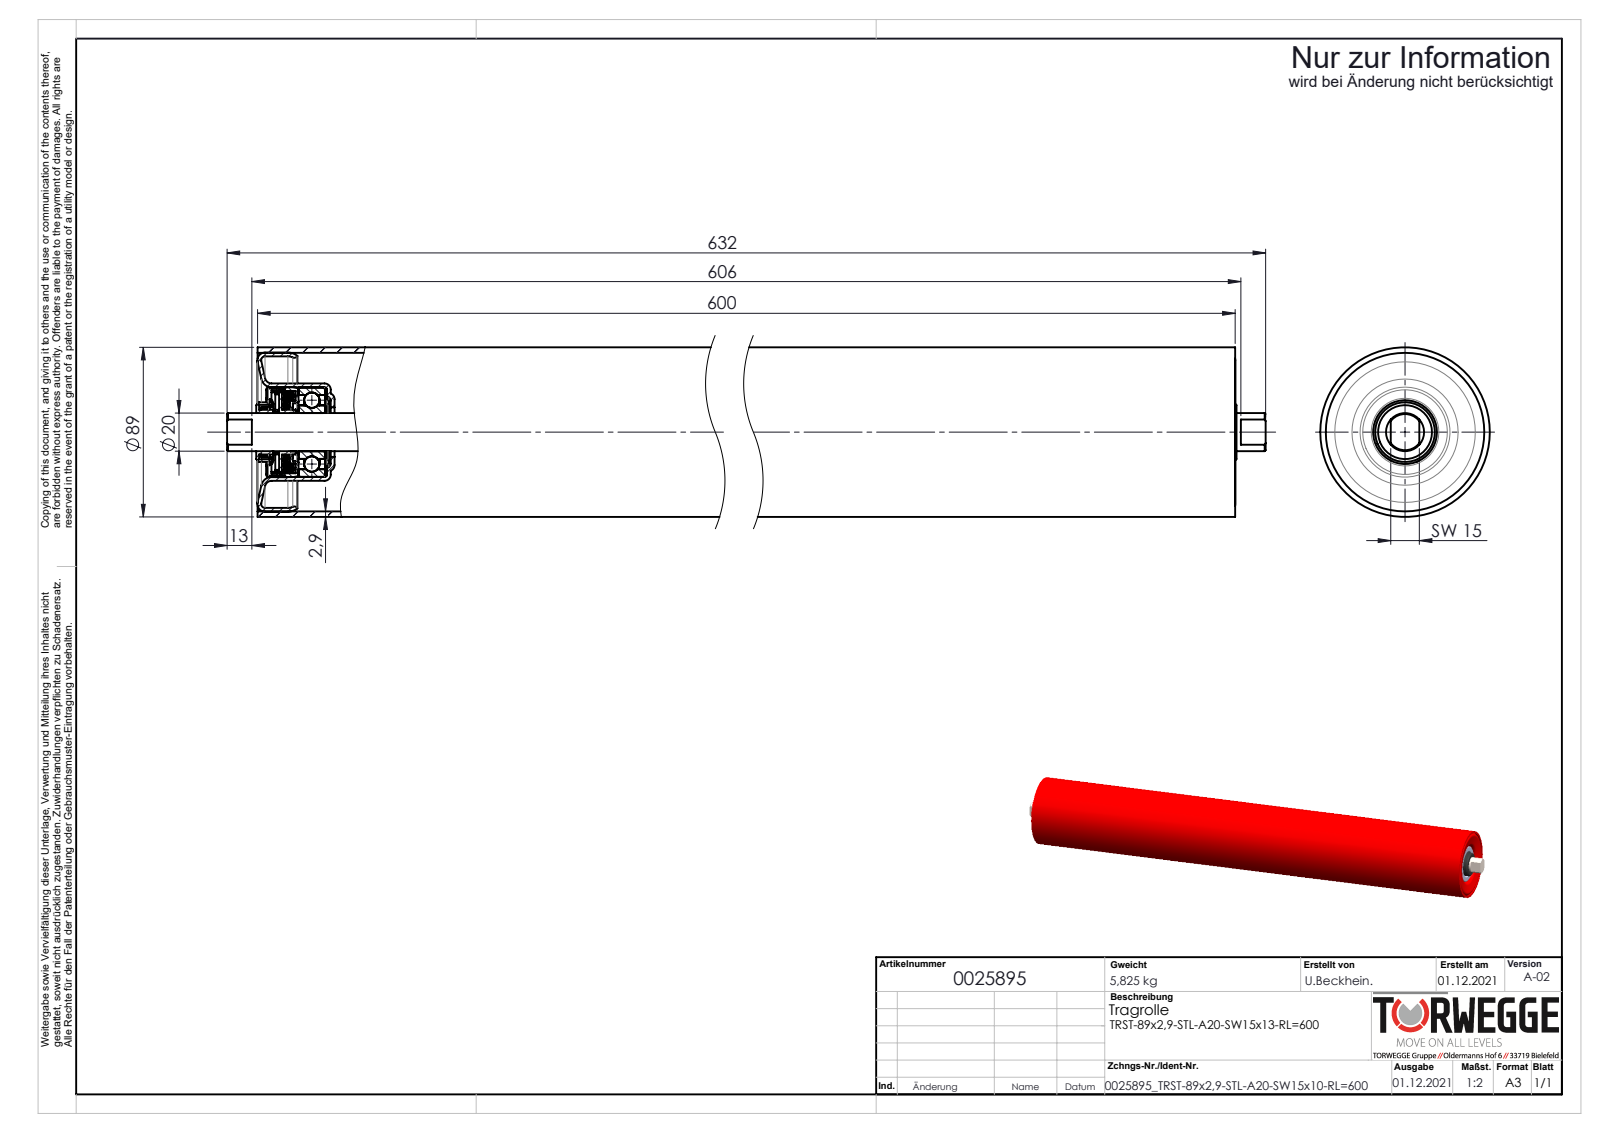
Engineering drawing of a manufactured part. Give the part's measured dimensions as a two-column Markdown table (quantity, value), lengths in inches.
| quantity | value |
| --- | --- |
| part name | 0025895 |
| STEP written by | SolidWorks 2020 (AUTOMOTIVE_DESIGN) |
| units | inches |
| bodies | 24 solids, 606 faces (114 planar, 244 cylindrical, 248 other) |
| overall size | 24.882 × 3.504 × 3.504 |
| volume | 50.09 in³ |
| surface area | 807.9 in² |
| round holes (diameter × count) | 0.079 × 4, 0.748 × 1, 0.772 × 1, 0.787 × 1, 0.799 × 1, 0.827 × 1, 0.846 × 1, 0.984 × 1, 0.992 × 1, 1.024 × 1, 1.11 × 1, 1.126 × 1 |
| round bosses / shafts (diameter × count) | 0.941 × 2, 3.504 × 1, 3.287 × 1, 2.012 × 1, 1.858 × 1, 1.85 × 1, 1.831 × 1, 1.72 × 1 |
| partial cylindrical surfaces (radius × count) | 0.079 × 8, 0.531 × 1 |
| main face-to-face distances | 0.551, 21.379, 0.587, 21.343, 0.036, 20.791, 21.93, 0.402, 0.953, 0.989 |
| hole center spacings | 0.452, 0.453, 0.888, 0.157, 0.157, 0.844, 0.905 |
